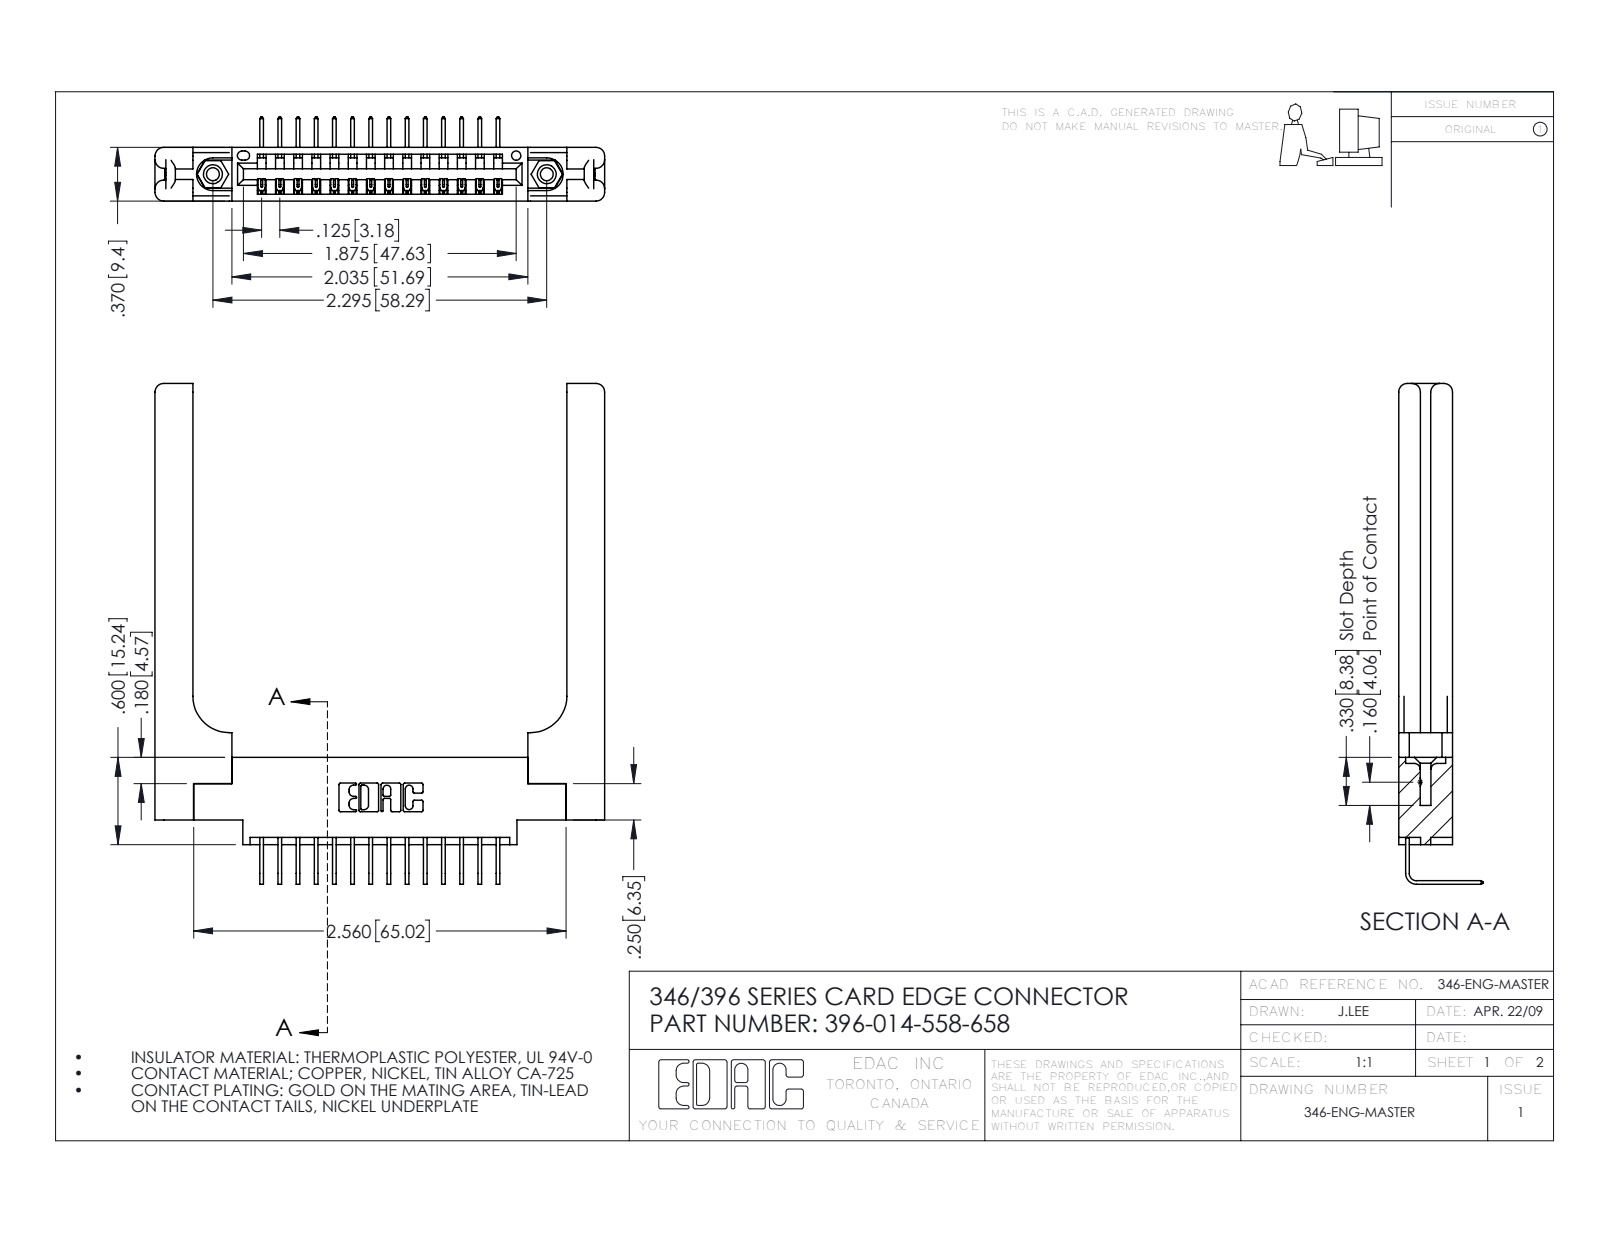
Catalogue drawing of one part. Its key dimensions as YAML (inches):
part_name: "345-292-001_558 Tail - 2; 396-014-558-658; 346-220-058_345-220-058; 345-250-001_345-250-001-102 (+1 more)"
step_written_by: "SolidWorks 2016 (CONFIG_CONTROL_DESIGN)"
units: inches
bodies: {solids: 19, faces: 1222, planar: 816, cylindrical: 346, other: 60}
overall_size: [3.443, 3.091, 0.58]
volume: 0.899
surface_area: 22.2
round_holes:
  - {diameter: 0.089, count: 2}
  - {diameter: 0.125, count: 2}
  - {diameter: 0.156, count: 2}
  - {diameter: 0.064, count: 1}
round_bosses_or_shafts:
  - {diameter: 0.155, count: 2}
partial_cylinders:
  - {radius: 0.006, count: 28}
  - {radius: 0.01, count: 22}
  - {radius: 0.06, count: 16}
  - {radius: 0.007, count: 6}
  - {radius: 0.031, count: 6}
  - {radius: 0.026, count: 3}
  - {radius: 0.03, count: 2}
  - {radius: 0.031, count: 2}
face_to_face_distances: [0.37, 0.15, 0.072, 0.148, 0.322, 0.048, 0.22, 0.25, 0.102, 0.173]
hole_center_spacings: [0.246, 2.089, 2.295]
